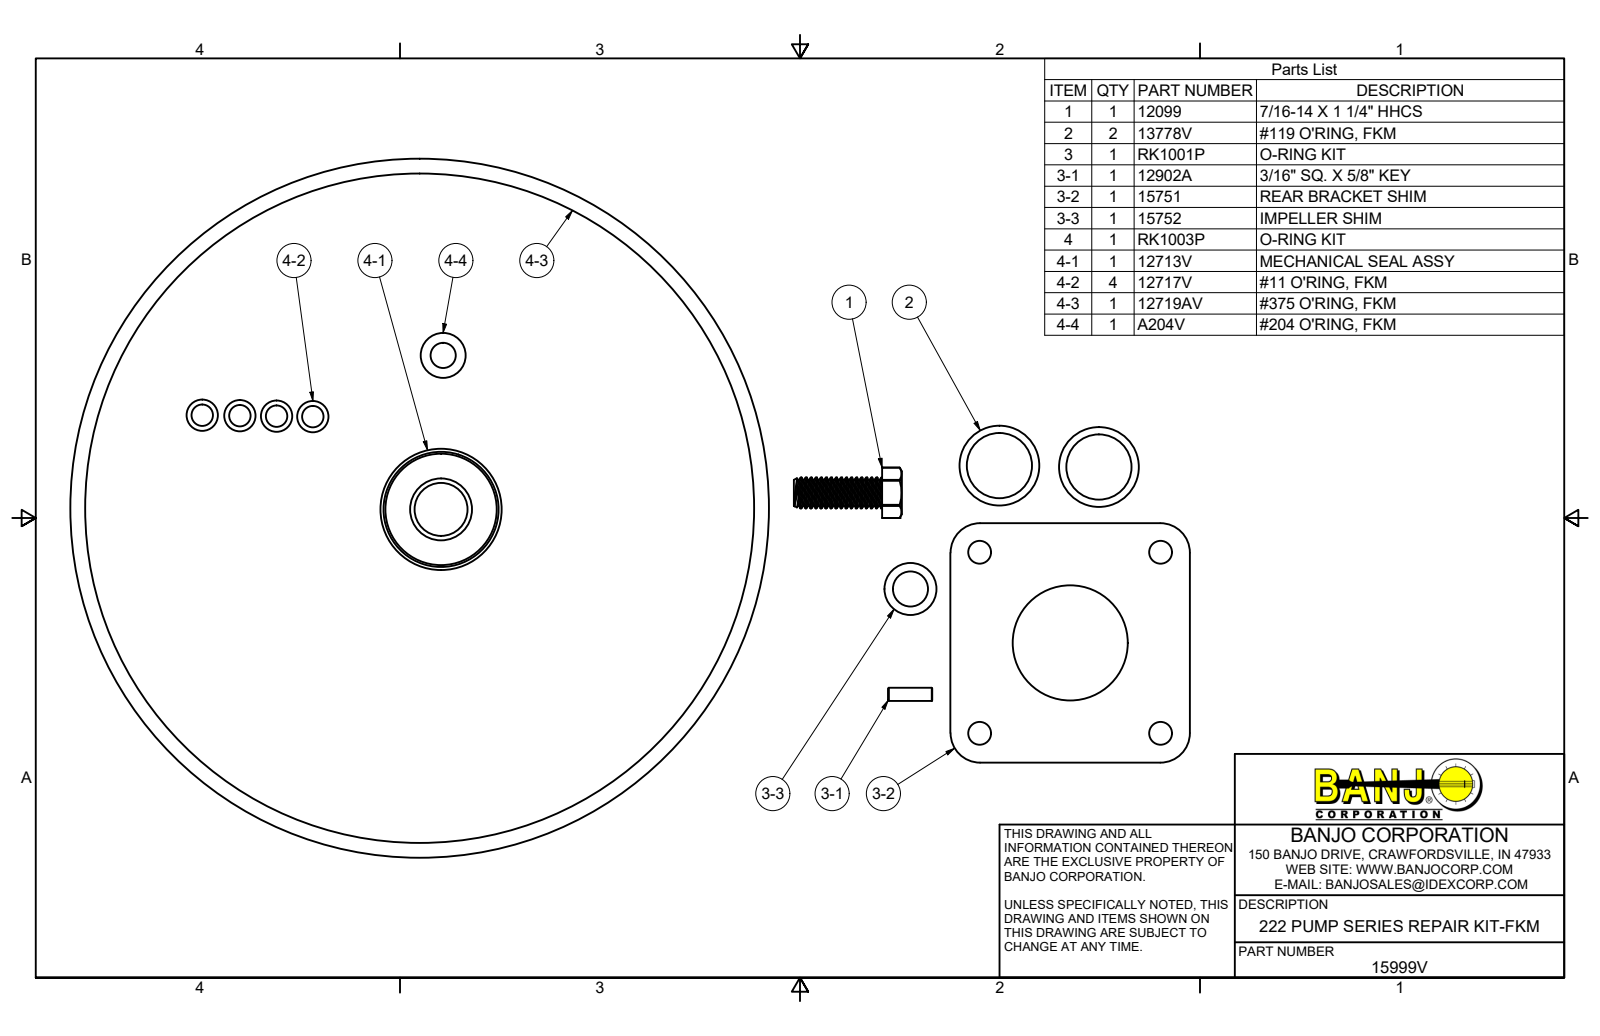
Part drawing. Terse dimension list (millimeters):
name: 15999V; 12099; 13778V; RK1001P (+8 more)
written by: Autodesk Inventor 2019 (AP242_MANAGED_MODEL_BASED_3D_ENGINEERING_MIM_LF)
unit: mm
bodies: 14 solids, 163 faces (43 planar, 66 cylindrical, 54 other)
size: 402.8 × 251.3 × 58.6
volume: 46 930 mm³; area: 38 840 mm²
holes: 4× ⌀8.2, 1× ⌀12.7, 1× ⌀19.1, 1× ⌀20.7, 1× ⌀22.2, 1× ⌀25.4, 1× ⌀41.4
bosses: 17× ⌀9.6, 1× ⌀43.7, 1× ⌀40, 1× ⌀34.9, 1× ⌀33.4, 1× ⌀33.1, 1× ⌀28.6, 1× ⌀27
rounds: 4× R10.7, 1× R4.8, 1× R9
face distances: 0.8, 54.7, 55.5, 9.7, 45, 45.8, 29.5, 39.1, 15.6, 6
hole spacings: 65.1, 46.1, 92.1, 28.2, 46, 46.1, 57.6, 60.7
